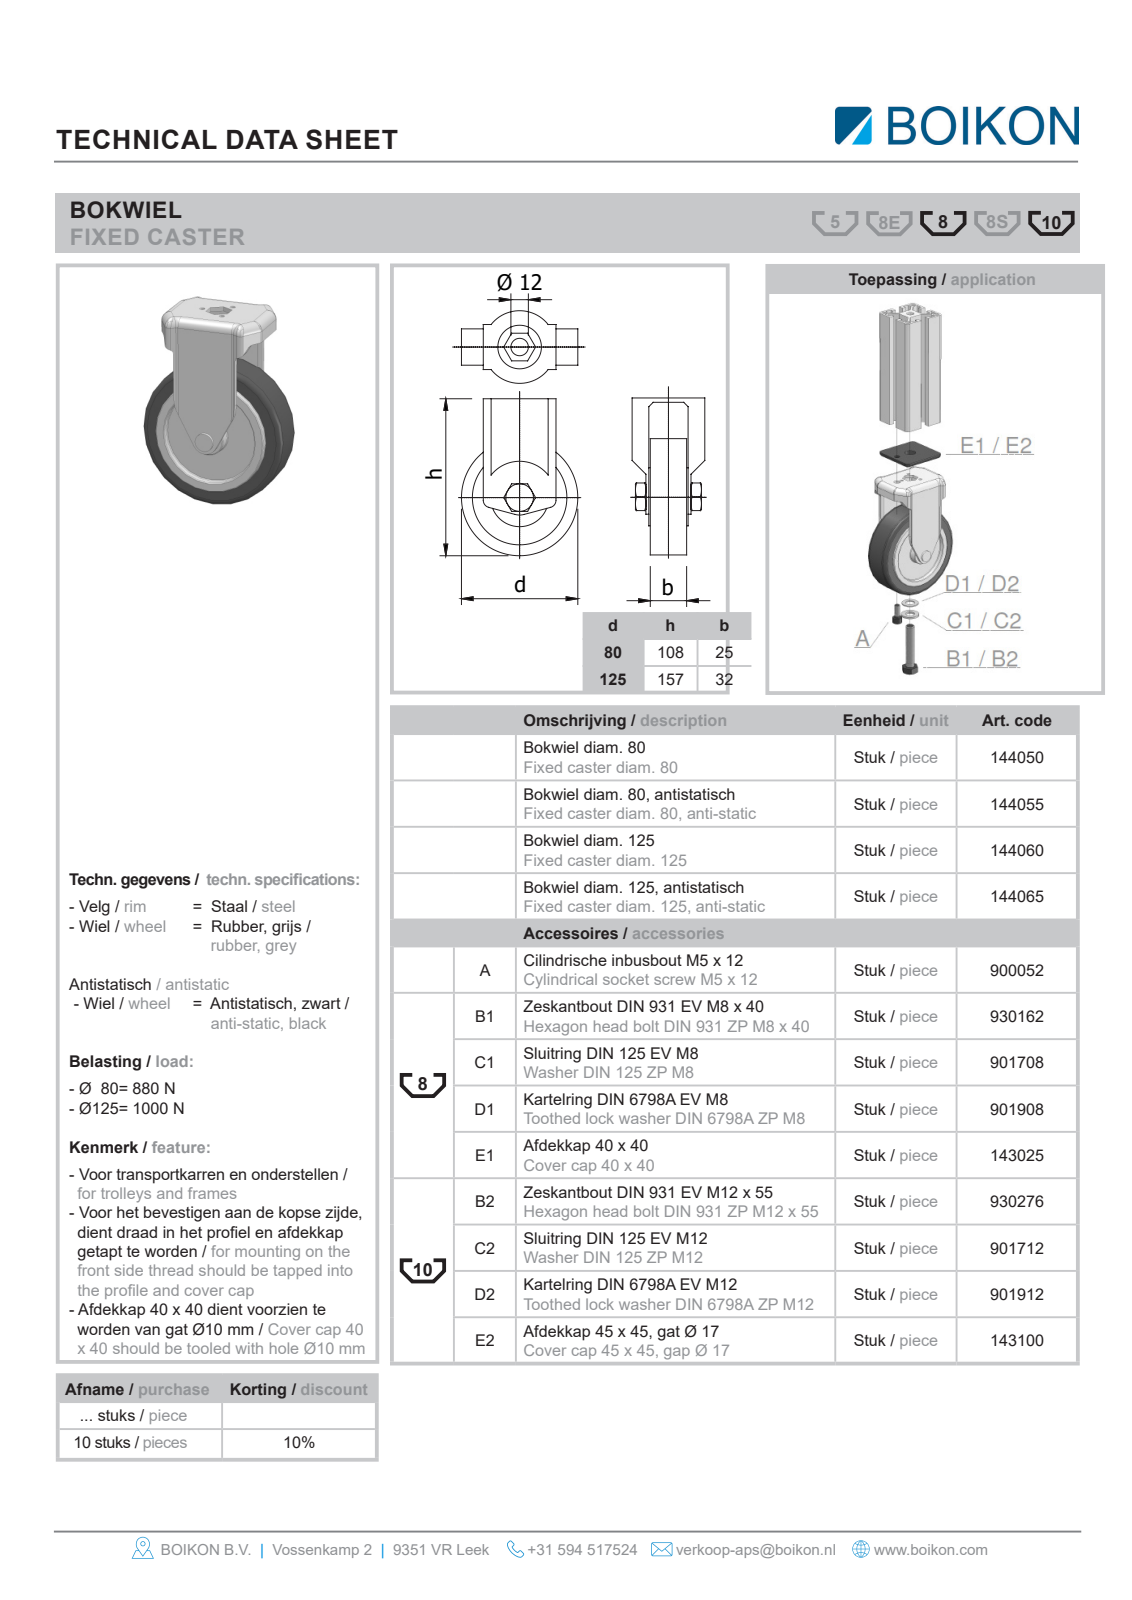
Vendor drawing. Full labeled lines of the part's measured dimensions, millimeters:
Part name (STEP PRODUCT): Root; 144050Bokwiel diam. 80BOIKON0
STEP written by: HiCAD 2013 1802.4 Build 509 (AUTOMOTIVE_DESIGN)
Units: millimetres
Bodies: 1 solid, 163 faces (60 planar, 60 cylindrical, 43 other)
Overall size (bounding box): 108 × 80 × 47.17
Volume: 141 013 mm³ · Surface area: 34 424 mm²
Round holes (diameter × count): ⌀3 ×3, ⌀52 ×1
Round bosses / shafts (diameter × count): ⌀80 ×1, ⌀62 ×1, ⌀18 ×1, ⌀10 ×1
Partial cylindrical surfaces — rounded edges, fillets, slot ends (radius × count): R5 ×16, R2.5 ×12, R2 ×6, R20 ×2, R7 ×1
Main face-to-face distances: 2.5, 30, 32.5, 40.5, 8, 10.5, 4, 10, 33, 7.5
Hole centre spacings: 16.46, 16.5, 16.55
